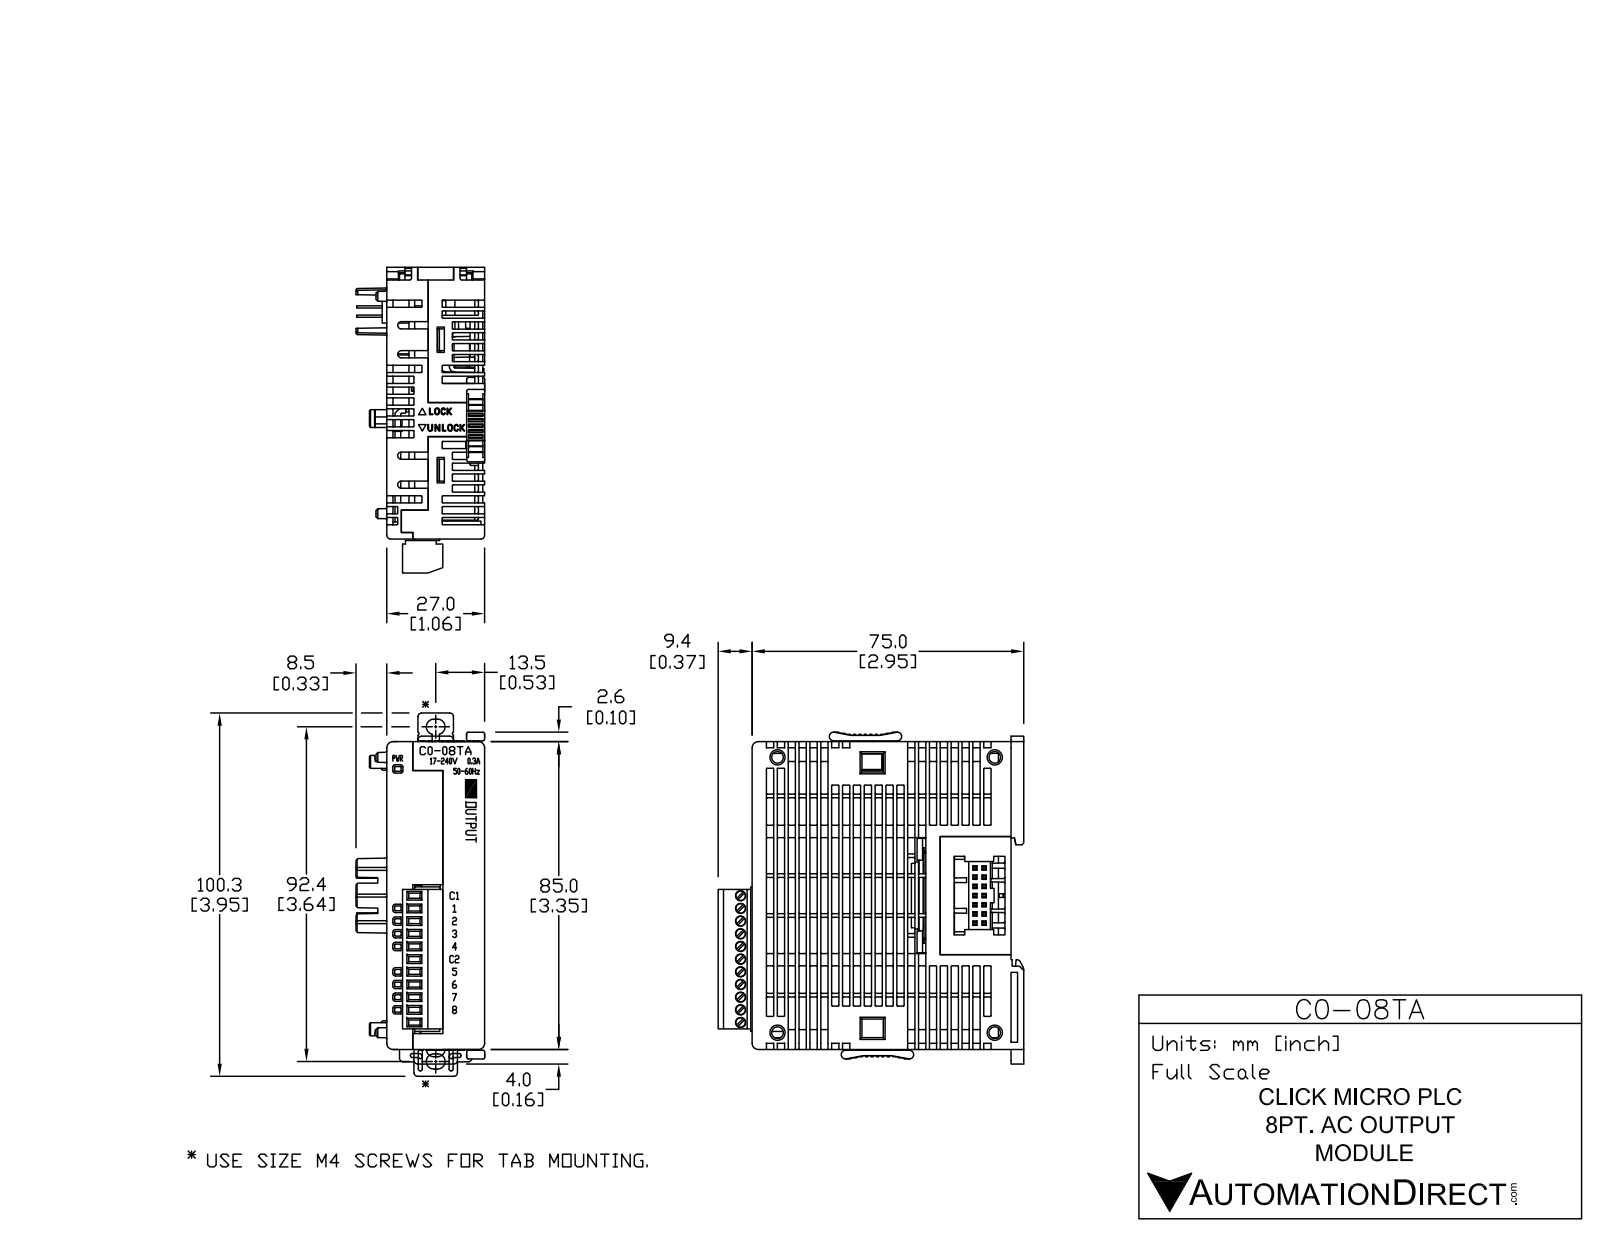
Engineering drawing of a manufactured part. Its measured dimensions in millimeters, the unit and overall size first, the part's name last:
Units: millimetres
Overall size (bounding box): 91.6 × 84.4 × 35.55
Round holes (diameter × count): ⌀1 ×11, ⌀2.8 ×11, ⌀3.2 ×4, ⌀2 ×2
Round bosses / shafts (diameter × count): ⌀2.6 ×11, ⌀1.9 ×1
Partial cylindrical surfaces — rounded edges, fillets, slot ends (radius × count): R0.2 ×570, R0.5 ×43, R0.3 ×22, R1 ×18, R1.2 ×12, R2.8 ×11, R1.7 ×6, R2.1 ×4
Main face-to-face distances: 27.01, 0.5, 0.51, 26.5, 71.5, 1.7, 85, 26.3, 26.81, 84.5
Hole centre spacings: 3.5, 7, 10.5, 14, 17.5, 21, 24.5, 28
Volume: 162 505 mm³ · Surface area: 31 767 mm²
Bodies: 1 solid, 3689 faces (2637 planar, 968 cylindrical, 84 other)
Part name (STEP PRODUCT): C0-08TA
STEP written by: SolidWorks 2009 (AUTOMOTIVE_DESIGN)
